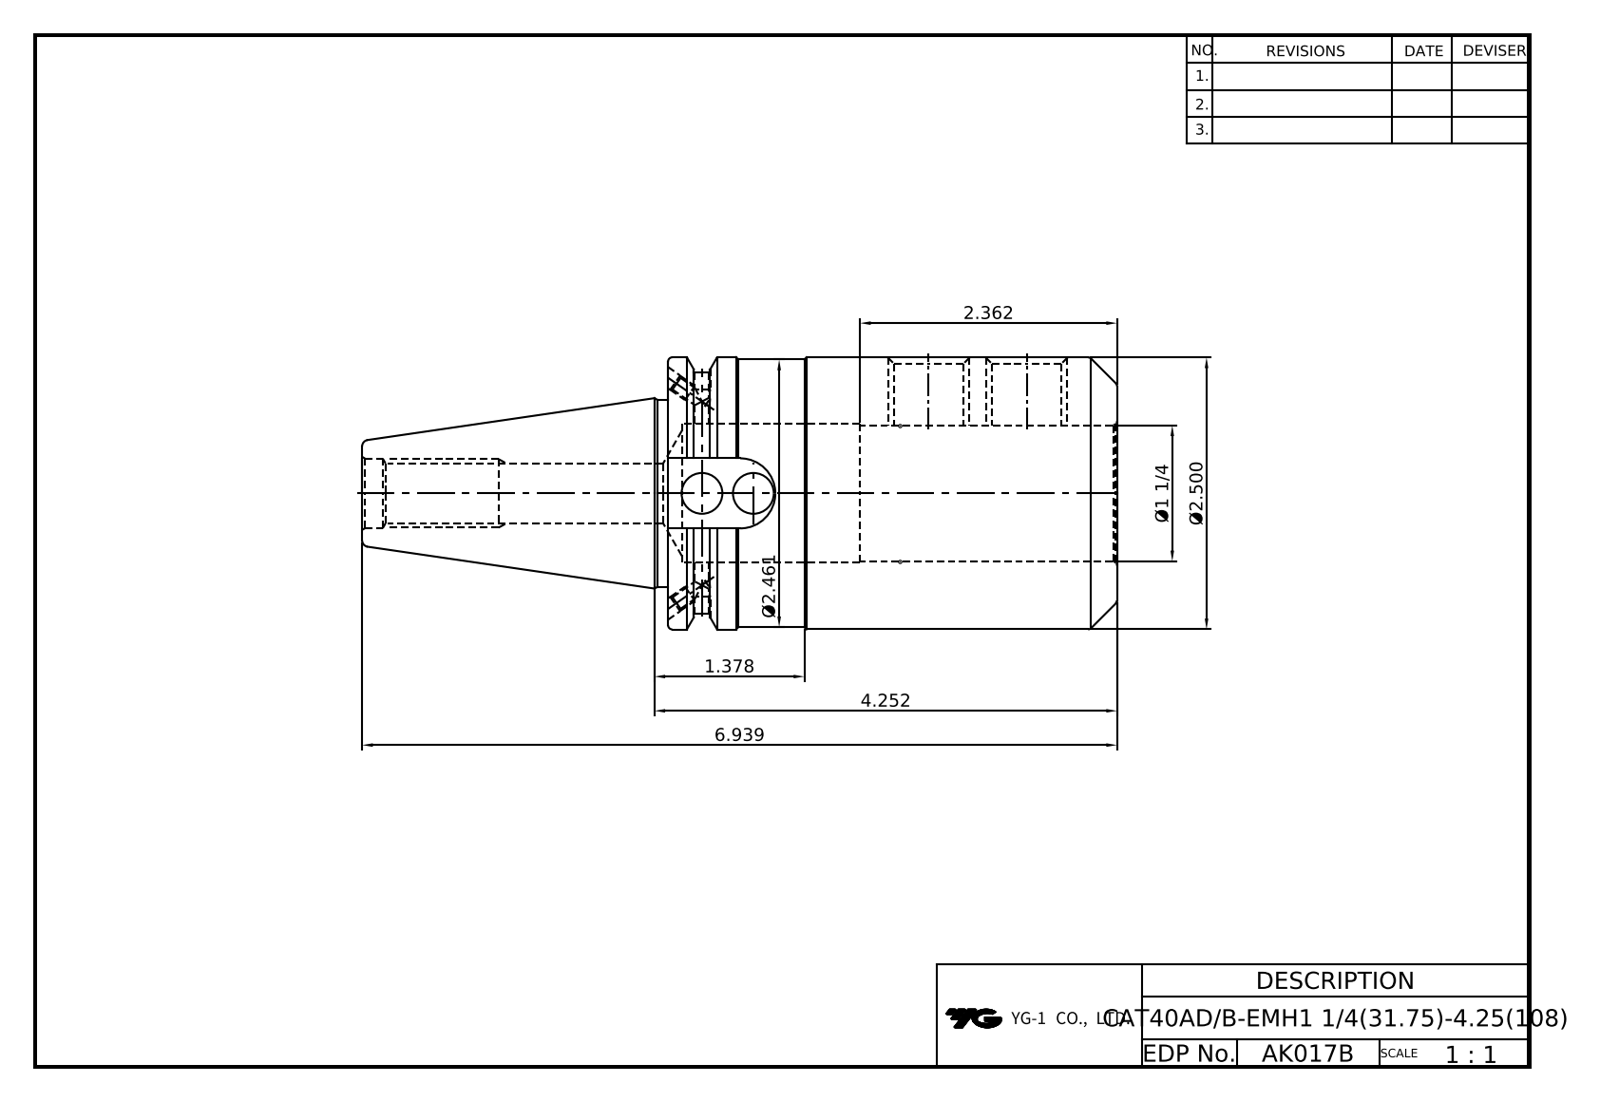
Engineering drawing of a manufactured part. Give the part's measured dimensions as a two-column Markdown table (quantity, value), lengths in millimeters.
| quantity | value |
| --- | --- |
| part name | LO-CAT40ADB-EMH31.75-108 |
| STEP written by | Autodesk Inventor 2025 (AUTOMOTIVE_DESIGN) |
| units | millimeters |
| bodies | 1 solid, 93 faces (34 planar, 32 cylindrical, 27 other) |
| overall size | 176.25 × 63.5 × 63.5 |
| volume | 285 574 mm³ |
| surface area | 48 874 mm² |
| round holes (diameter × count) | 3.24 × 4, 4 × 2, 4.2 × 2, 17.32 × 2, 9.53 × 1, 13.39 × 1, 16.3 × 1, 31.75 × 1, 32.95 × 1 |
| round bosses / shafts (diameter × count) | 63.5 × 1, 62.5 × 1, 43.6 × 1 |
| partial cylindrical surfaces (radius × count) | 8.19 × 1, 28.15 × 1 |
| main face-to-face distances | 104.83, 3.23, 101.6, 47.6, 16.38, 71.42, 74.65, 176.25, 81.29, 9.87 |
| hole center spacings | 22.86 |
